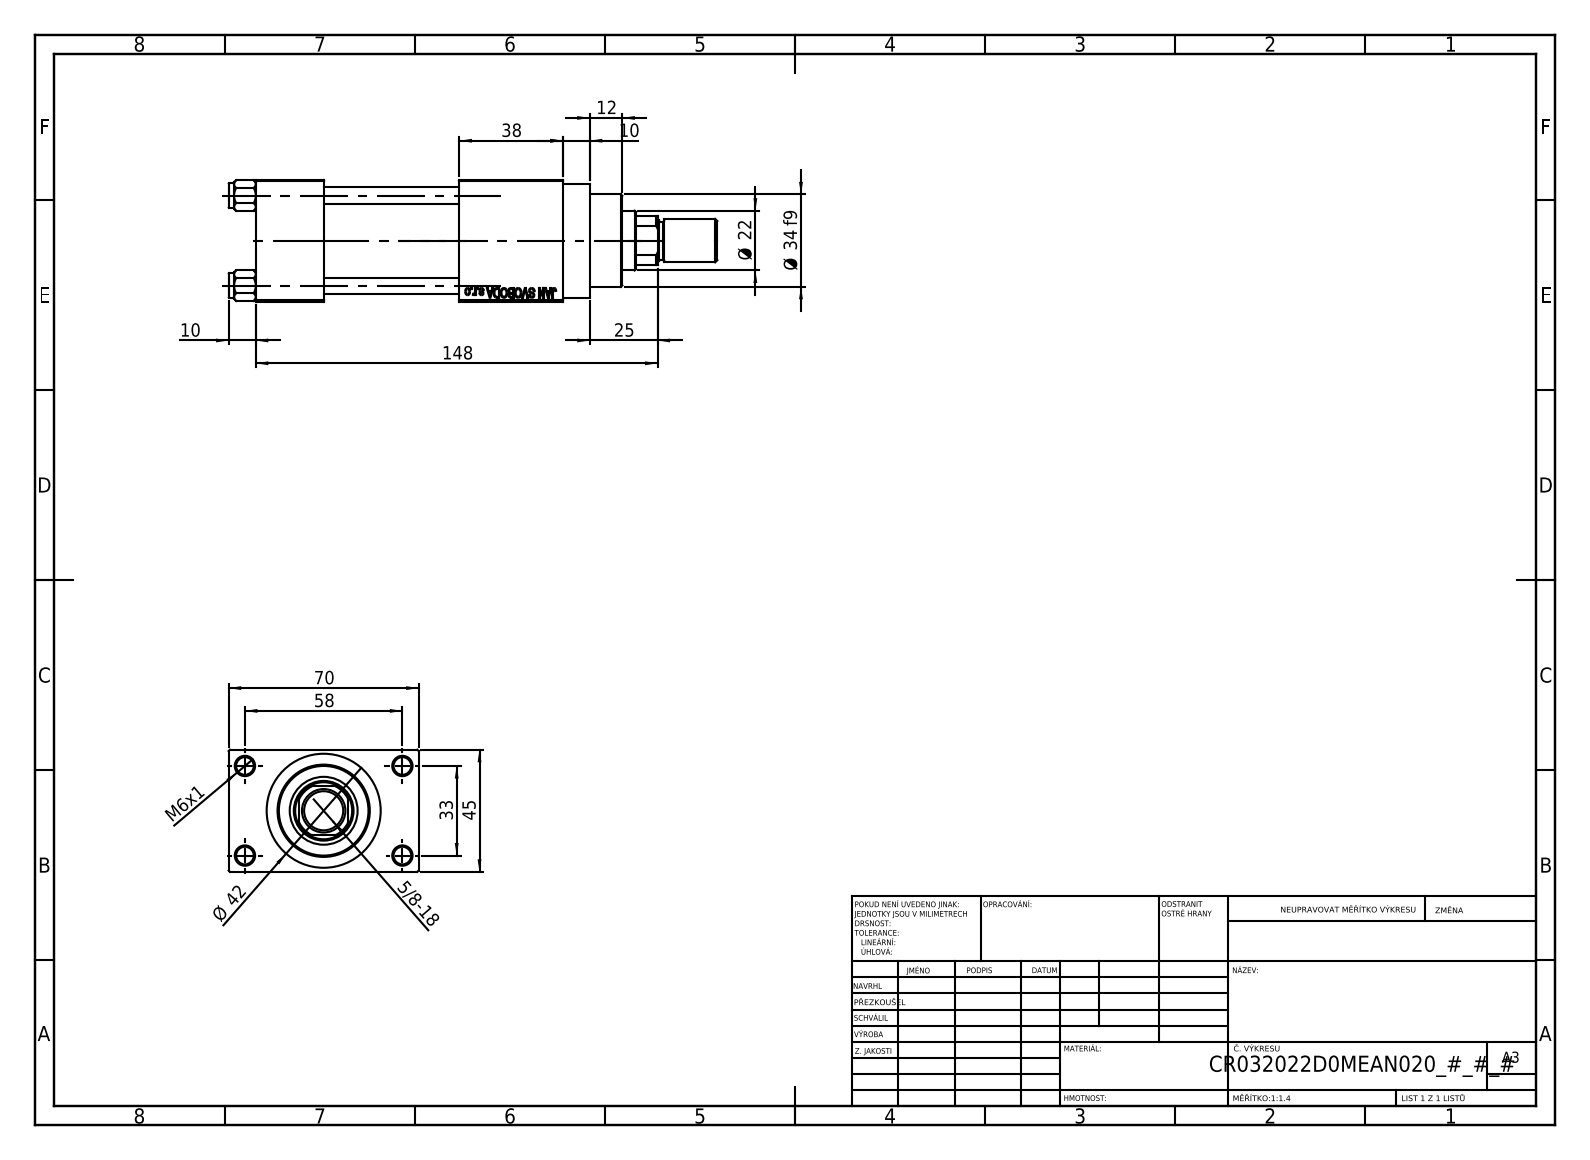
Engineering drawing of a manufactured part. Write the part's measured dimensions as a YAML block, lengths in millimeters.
part_name: "V215_VC_A; V215CR_VCP_D; V215CR_D_TYCINKA; NUT_M5_D (+2 more)"
step_written_by: "SolidWorks 2019 (CONFIG_CONTROL_DESIGN)"
units: millimeters
bodies: {solids: 12, faces: 1117, planar: 500, cylindrical: 93, other: 524}
overall_size: [180, 70, 45]
volume: 248936
surface_area: 80995
round_holes:
  - {diameter: 6, count: 4}
  - {diameter: 6.5, count: 4}
  - {diameter: 7, count: 2}
  - {diameter: 13.16, count: 2}
  - {diameter: 20, count: 2}
  - {diameter: 10.5, count: 1}
  - {diameter: 22, count: 1}
  - {diameter: 24, count: 1}
  - {diameter: 25, count: 1}
  - {diameter: 32, count: 1}
  - {diameter: 33, count: 1}
round_bosses_or_shafts:
  - {diameter: 9, count: 4}
  - {diameter: 42, count: 1}
  - {diameter: 38, count: 1}
  - {diameter: 34, count: 1}
  - {diameter: 16, count: 1}
  - {diameter: 14, count: 1}
partial_cylinders:
  - {radius: 10.5, count: 1}
face_to_face_distances: [45, 25, 12.5, 57.5, 50, 75, 88, 70, 38, 113]
hole_center_spacings: [12.4, 23.48, 33.2, 33.37, 35.35, 45.6, 56.35, 33]
